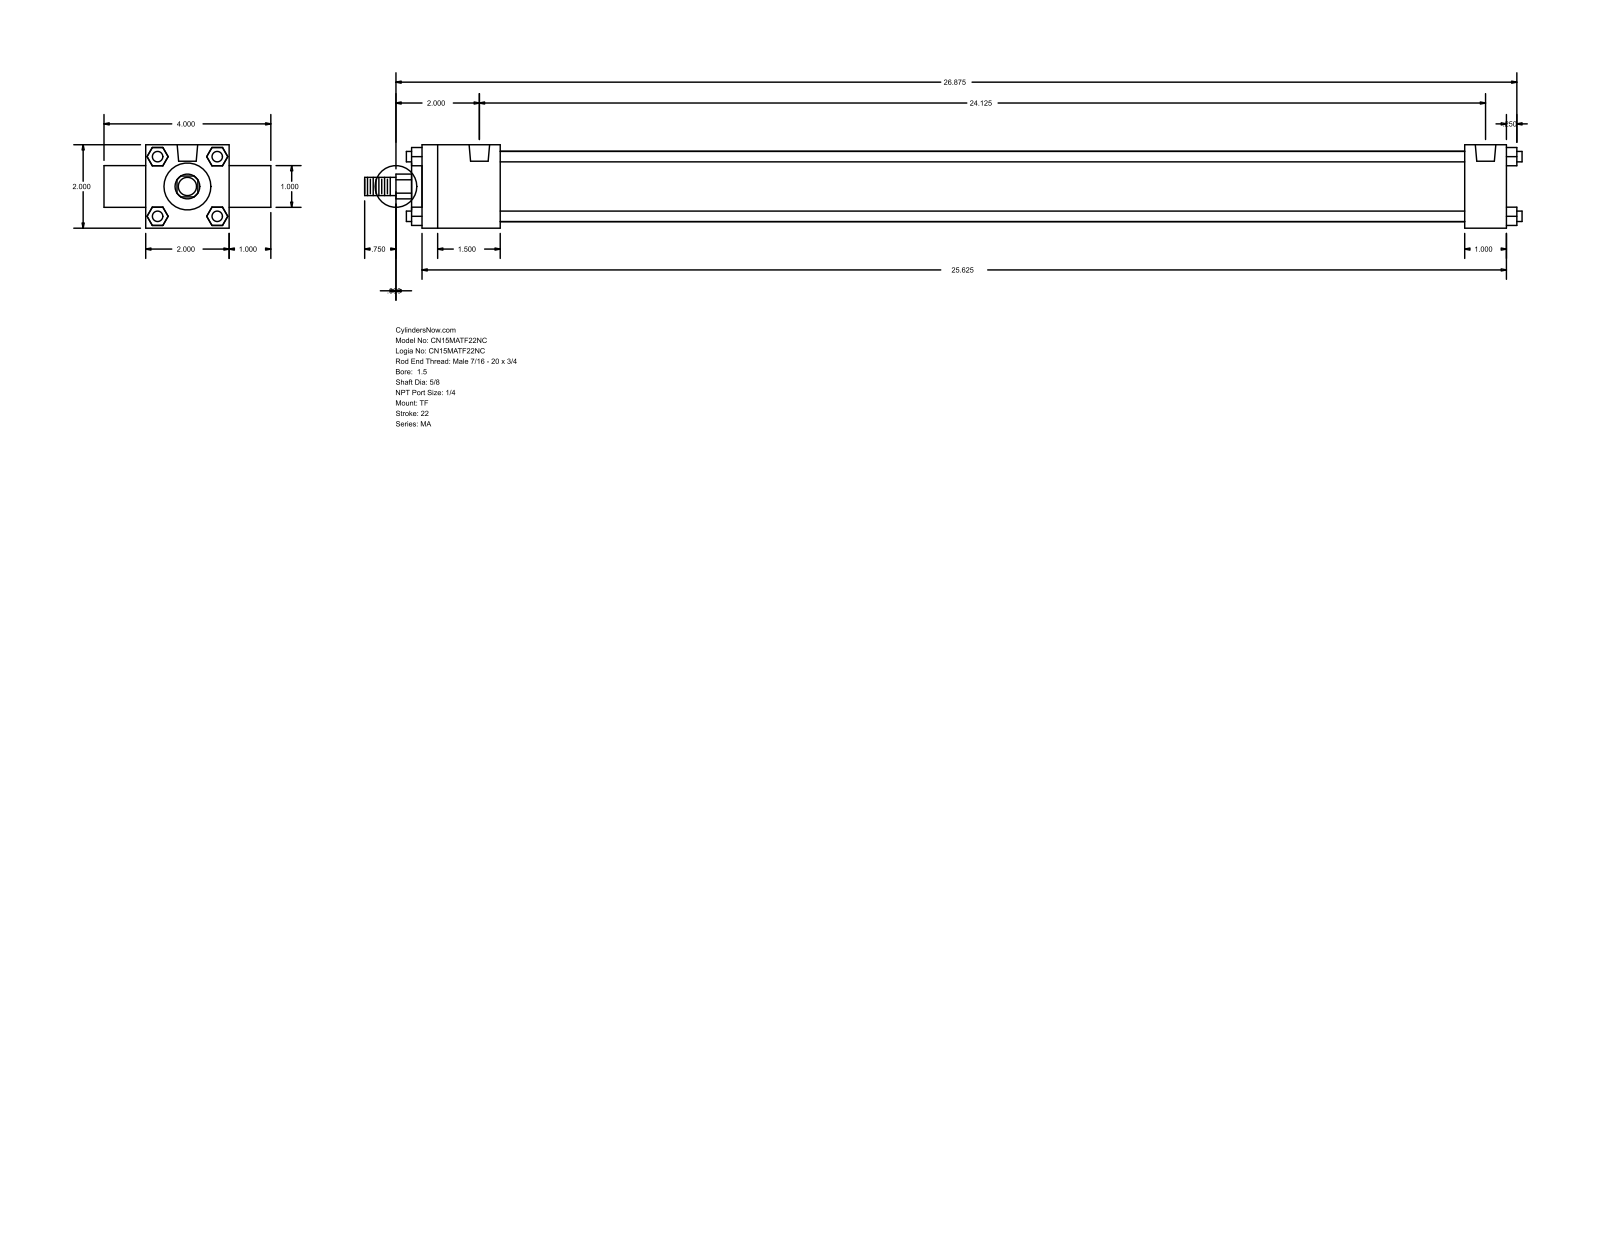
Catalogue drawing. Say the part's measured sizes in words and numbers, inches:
The part is named "MA_TF__0150_0.625". Its 3-D file was written by "GSSL Pune (CONFIG_CONTROL_DESIGN)". It is 0 solids with 120 faces: 92 planar, 28 cylindrical and 0 other. Overall it measures 27.75 by 4 by 2 inches. Round holes: 3 of diameter 0.313, 2 of diameter 0.492. Round bosses or shafts: 4 of diameter 0.25, 1 of diameter 1.69, 1 of diameter 1.125, 1 of diameter 1, 1 of diameter 0.625, 1 of diameter 0.437. Partial cylindrical surfaces (rounded edges, fillets, slot ends): 1 of radius 0.297. The main face-to-face distances are 2, 26, 1, 0.25, 26.25, 3, 1.875, 25, 23.125, 24.125. The hole center spacings are 24.125.
